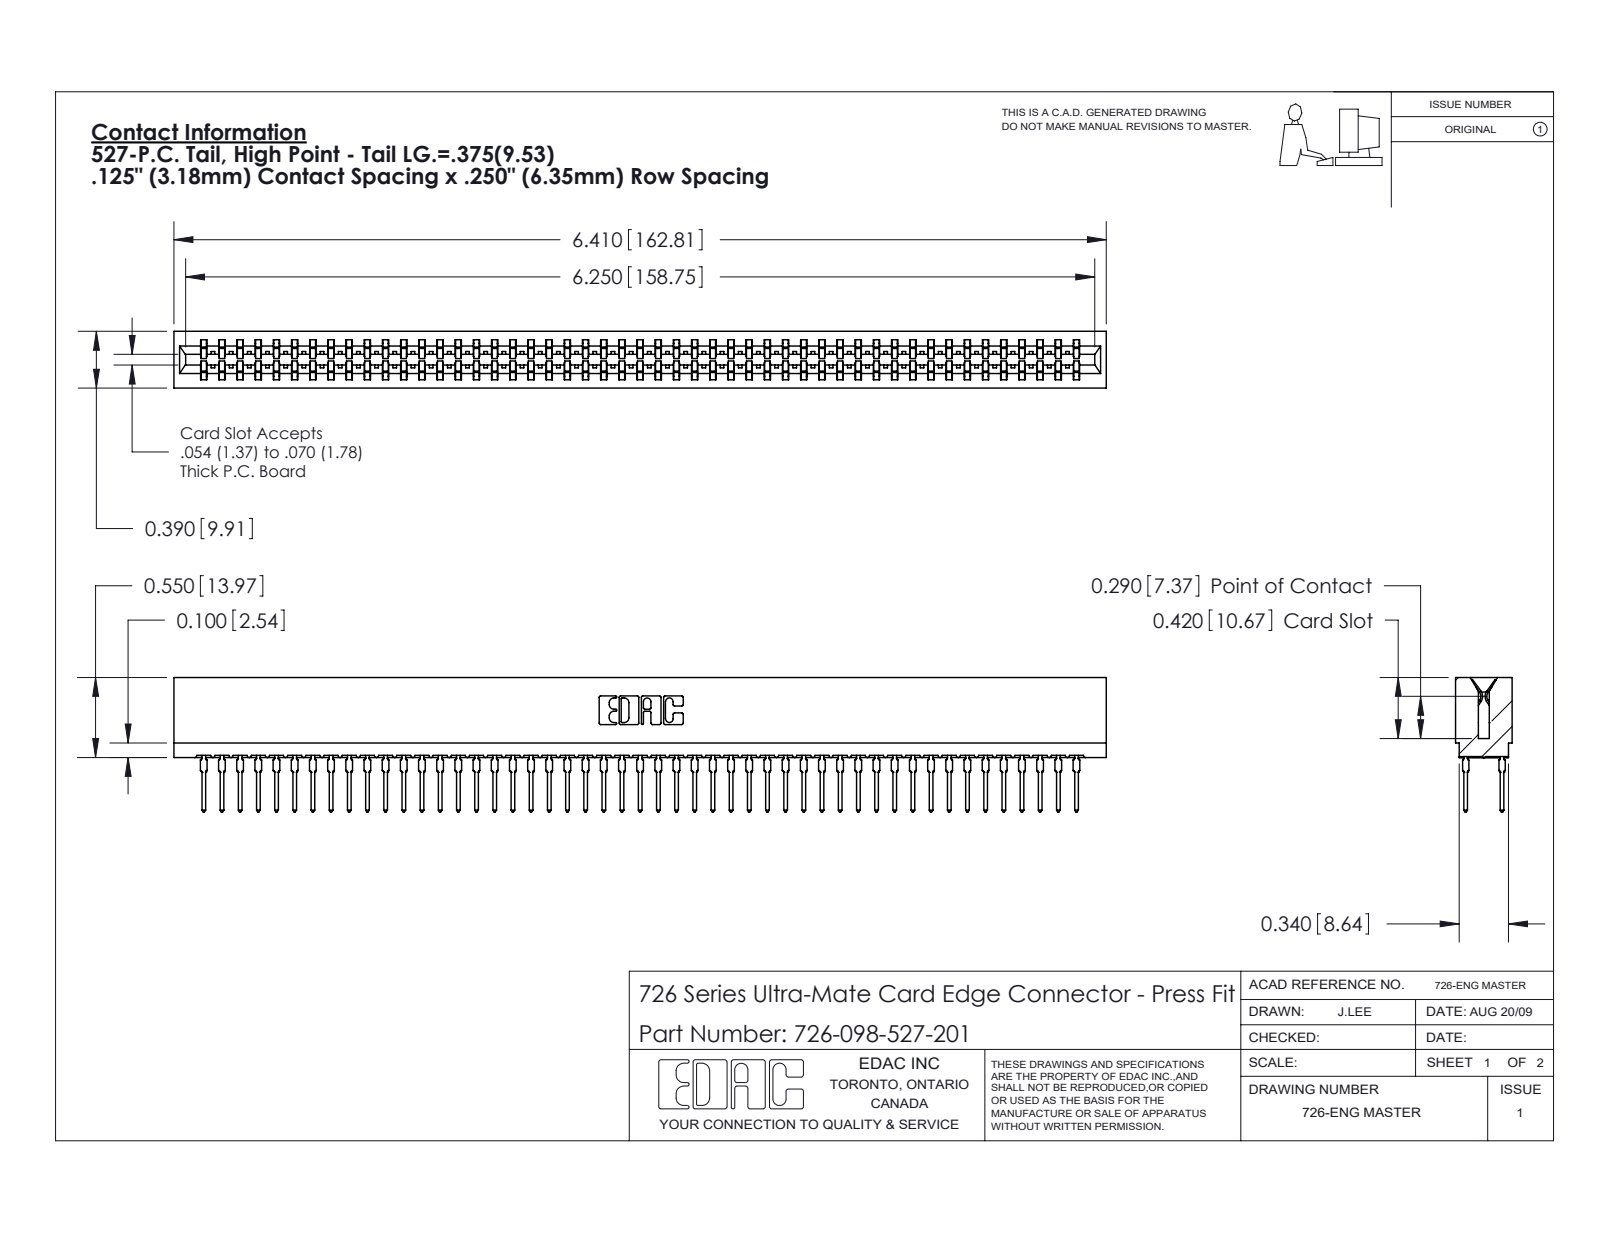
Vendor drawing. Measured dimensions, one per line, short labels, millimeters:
name: 746-292-001_527; 726-098-527-201; 726 Part_.515 Slot Depth - 01
written by: SolidWorks 2020 (CONFIG_CONTROL_DESIGN)
unit: mm
bodies: 99 solids, 8868 faces (4563 planar, 1757 cylindrical, 2548 other)
size: 162.8 × 23.5 × 9.9
volume: 15 100 mm³; area: 26 080 mm²
rounds: 196× R0.5, 50× R0.4, 22× R0.3, 8× R0.1, 8× R0.3, 6× R0.2, 6× R0.8, 3× R0.7
face distances: 1.4, 8.5, 0.6, 7.8, 9.9, 7, 6.4, 2.1, 9.3, 0.8
